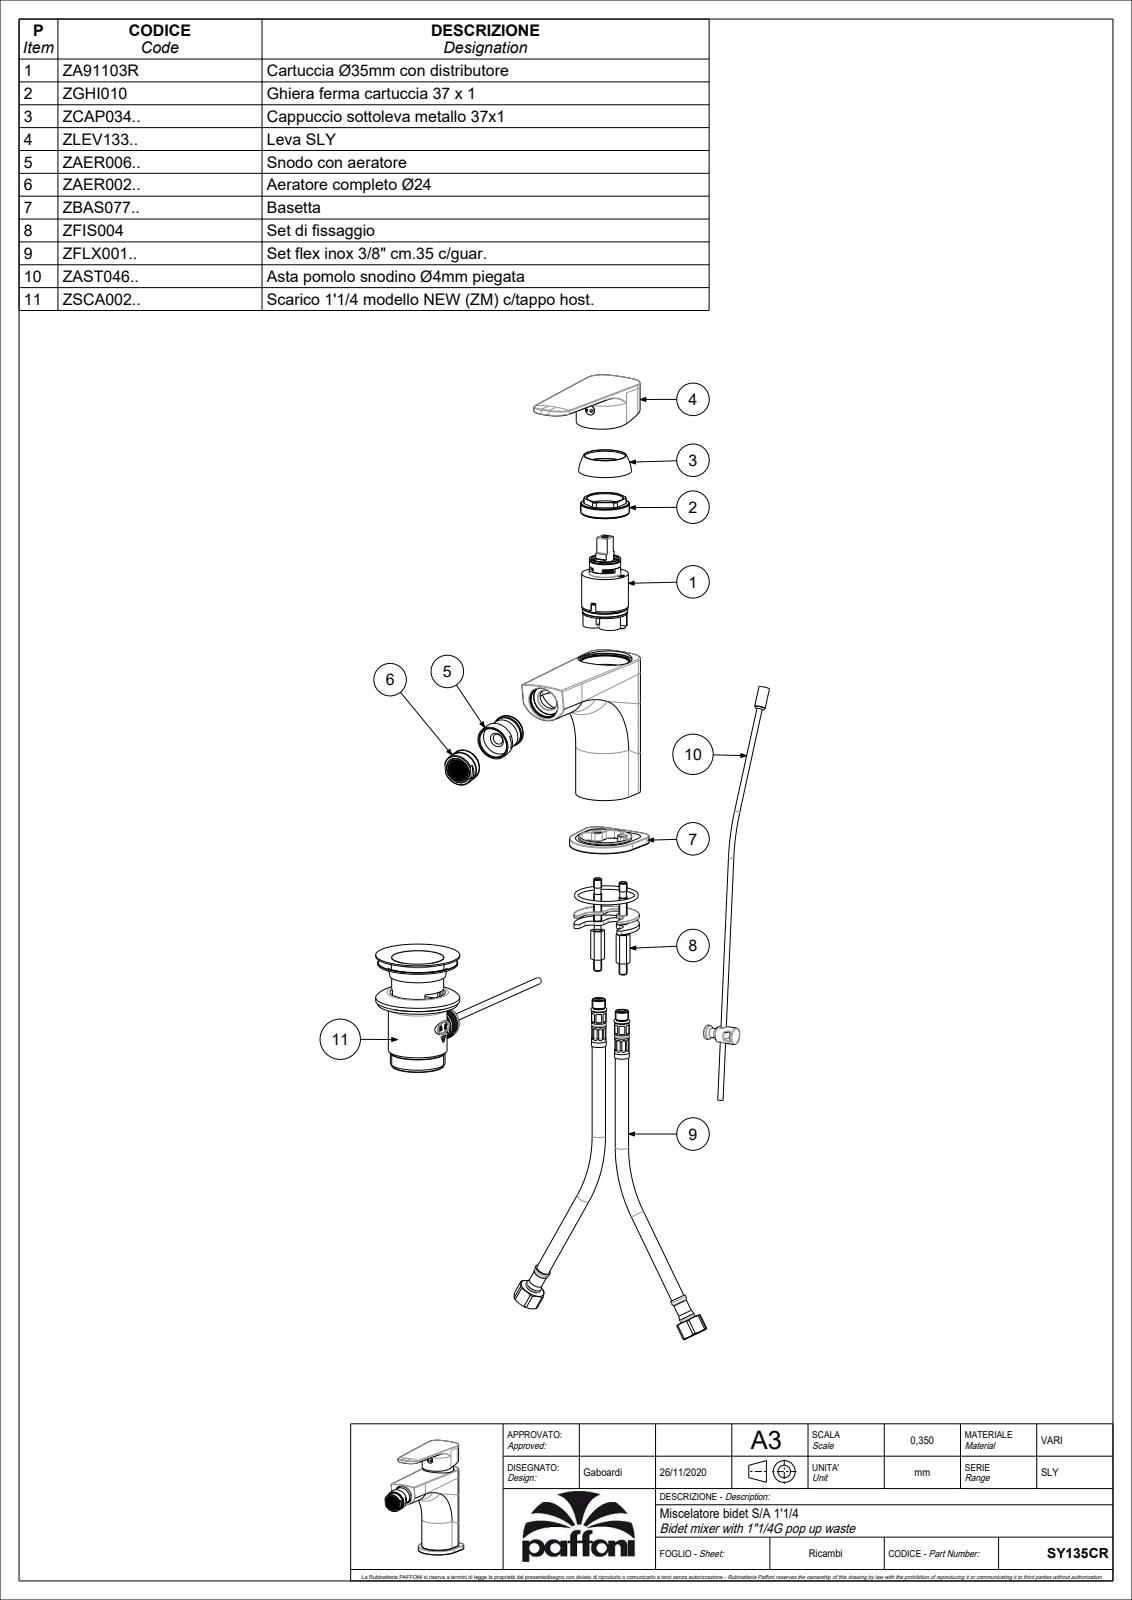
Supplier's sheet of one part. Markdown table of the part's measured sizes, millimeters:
| quantity | value |
| --- | --- |
| part name | SY135CR |
| STEP written by | CREO PARAMETRIC BY PTC INC, 2020044 (CONFIG_CONTROL_DESIGN) |
| units | millimeters |
| bodies | 4 solids, 2888 faces (2112 planar, 402 cylindrical, 374 other) |
| overall size | 163.66 × 141.8 × 53.82 |
| volume | 170 925 mm³ |
| surface area | 110 272 mm² |
| round holes (diameter × count) | 9 × 5, 5.5 × 3, 8 × 3, 12 × 3, 4 × 2, 4.6 × 2, 6.2 × 2, 7 × 2, 11 × 2, 16 × 2, 3 × 1, 3.3 × 1 |
| round bosses / shafts (diameter × count) | 10 × 3, 5 × 3, 10.8 × 2, 8.2 × 2, 6 × 2, 42 × 1, 40 × 1, 35 × 1 |
| partial cylindrical surfaces (radius × count) | 0.5 × 55, 0.15 × 11, 1.5 × 10, 0.3 × 9, 1 × 4, 5 × 4, 7 × 4, 10 × 4 |
| main face-to-face distances | 3, 5, 9.5, 59, 15, 6, 8.5, 2, 21.5, 6.5 |
| hole center spacings | 13.6, 0.5, 0.71, 1.12, 8.51, 8.6, 9.01, 11.18 |
